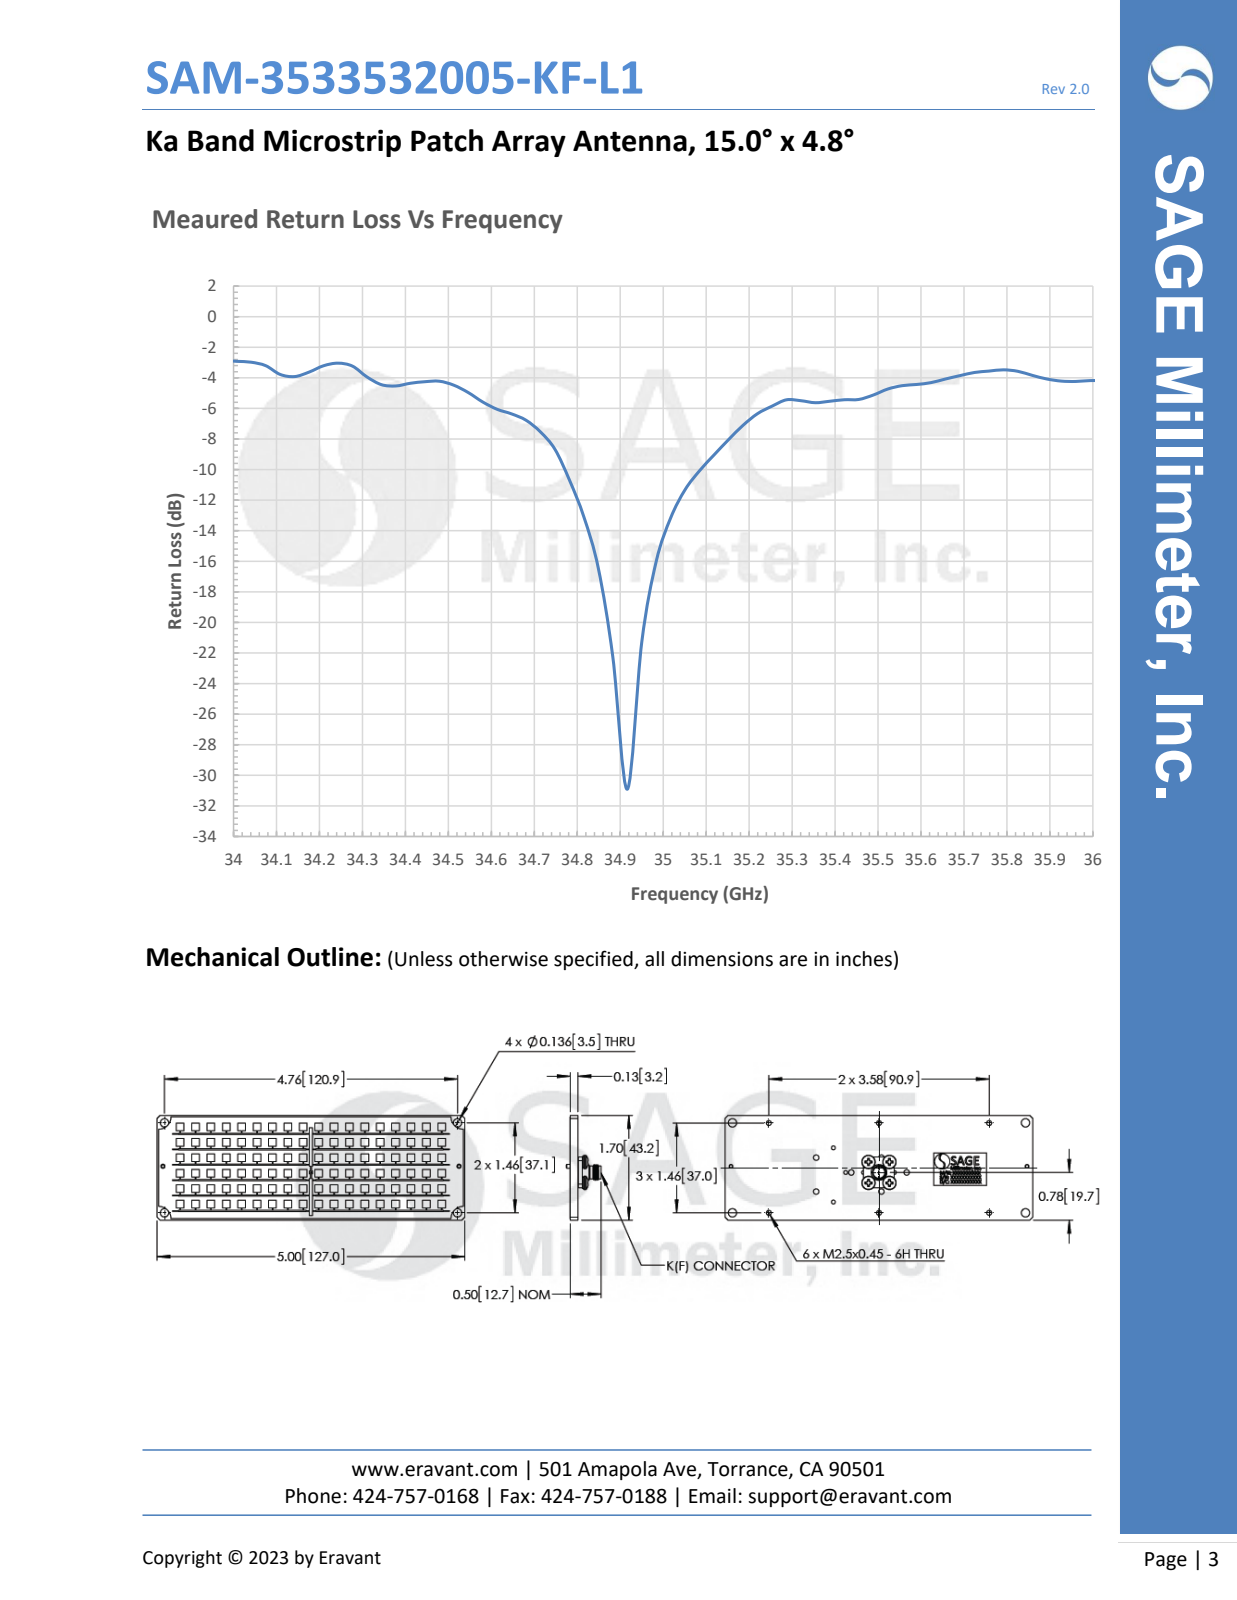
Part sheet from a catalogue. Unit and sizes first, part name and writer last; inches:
Units: inches
Overall size (bounding box): 5 × 1.7 × 0.563
Round holes (diameter × count): ⌀0.081 ×6, ⌀0.09 ×4, ⌀0.096 ×4, ⌀0.136 ×4, ⌀0.05 ×2, ⌀0.067 ×2, ⌀0.02 ×1, ⌀0.19 ×1
Round bosses / shafts (diameter × count): ⌀0.172 ×4, ⌀0.167 ×4, ⌀0.086 ×4, ⌀0.063 ×4, ⌀0.063 ×2, ⌀0.248 ×1, ⌀0.21 ×1, ⌀0.2 ×1
Partial cylindrical surfaces — rounded edges, fillets, slot ends (radius × count): R0.2 ×4
Main face-to-face distances: 0.125, 0.13, 1.7, 0.2, 0.195, 0.07, 5, 0.135, 0.065, 0.09
Hole centre spacings: 0.59, 1.79, 2.236, 2.251, 2.307, 2.38, 2.407, 2.505
Volume: 1.124 in³ · Surface area: 36.88 in²
Bodies: 13 solids, 553 faces (127 planar, 338 cylindrical, 88 other)
Part name (STEP PRODUCT): DMAM-28-121-1, DF
STEP written by: SolidWorks 2016 (AUTOMOTIVE_DESIGN)
